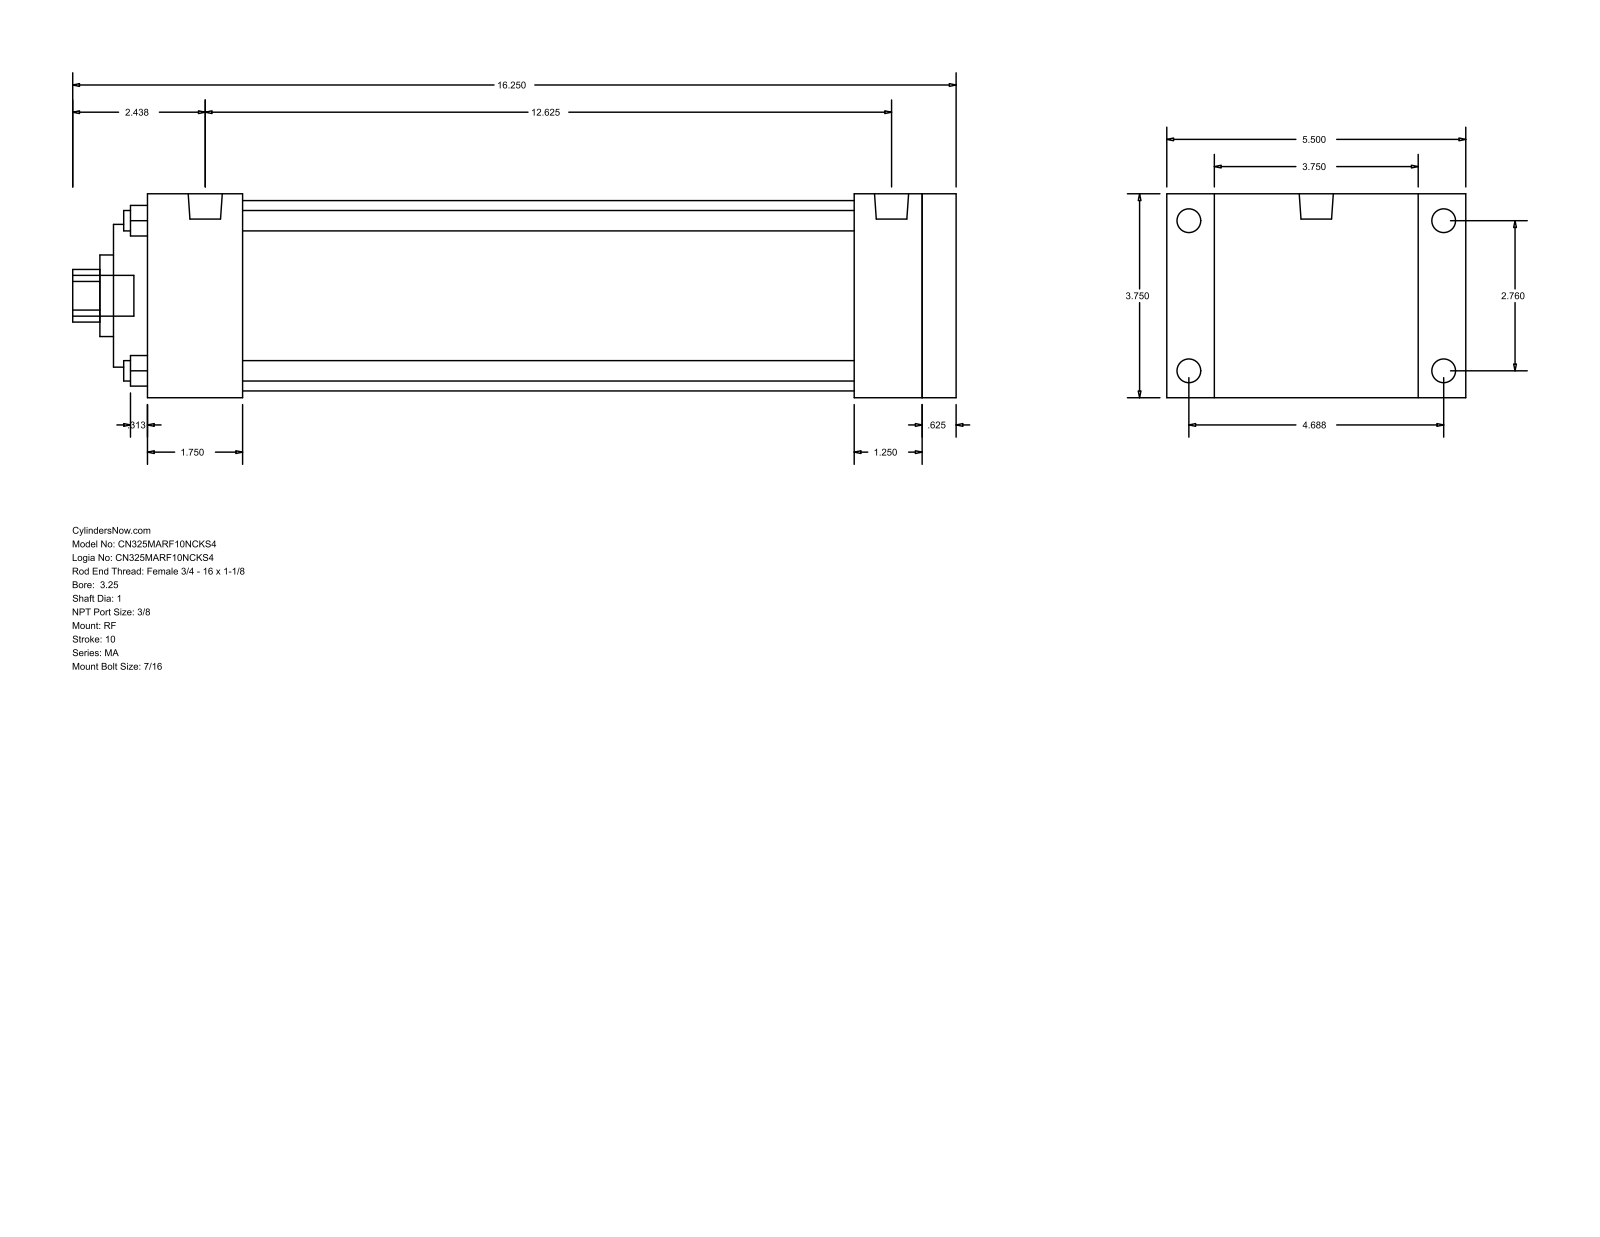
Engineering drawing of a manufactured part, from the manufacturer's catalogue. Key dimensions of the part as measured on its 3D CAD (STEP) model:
Part name (STEP PRODUCT): MA_RF__0325_1
STEP written by: GSSL Pune (CONFIG_CONTROL_DESIGN)
Units: millimetres
Bodies: 0 solids, 94 faces (65 planar, 29 cylindrical, 0 other)
Overall size (bounding box): 412.75 × 139.7 × 95.25
Round holes (diameter × count): ⌀9.53 ×4, ⌀25.4 ×1, ⌀38.1 ×1, ⌀66.67 ×1, ⌀88.9 ×1
Round bosses / shafts (diameter × count): ⌀11.11 ×8, ⌀15.93 ×2, ⌀19.05 ×1
Partial cylindrical surfaces — rounded edges, fillets, slot ends (radius × count): R12.29 ×1
Main face-to-face distances: 95.24, 377.83, 15.87, 361.96, 22.23, 117.47, 330.2, 31.76, 47.63, 44.46
Hole centre spacings: 49.57, 70.1, 99.14
